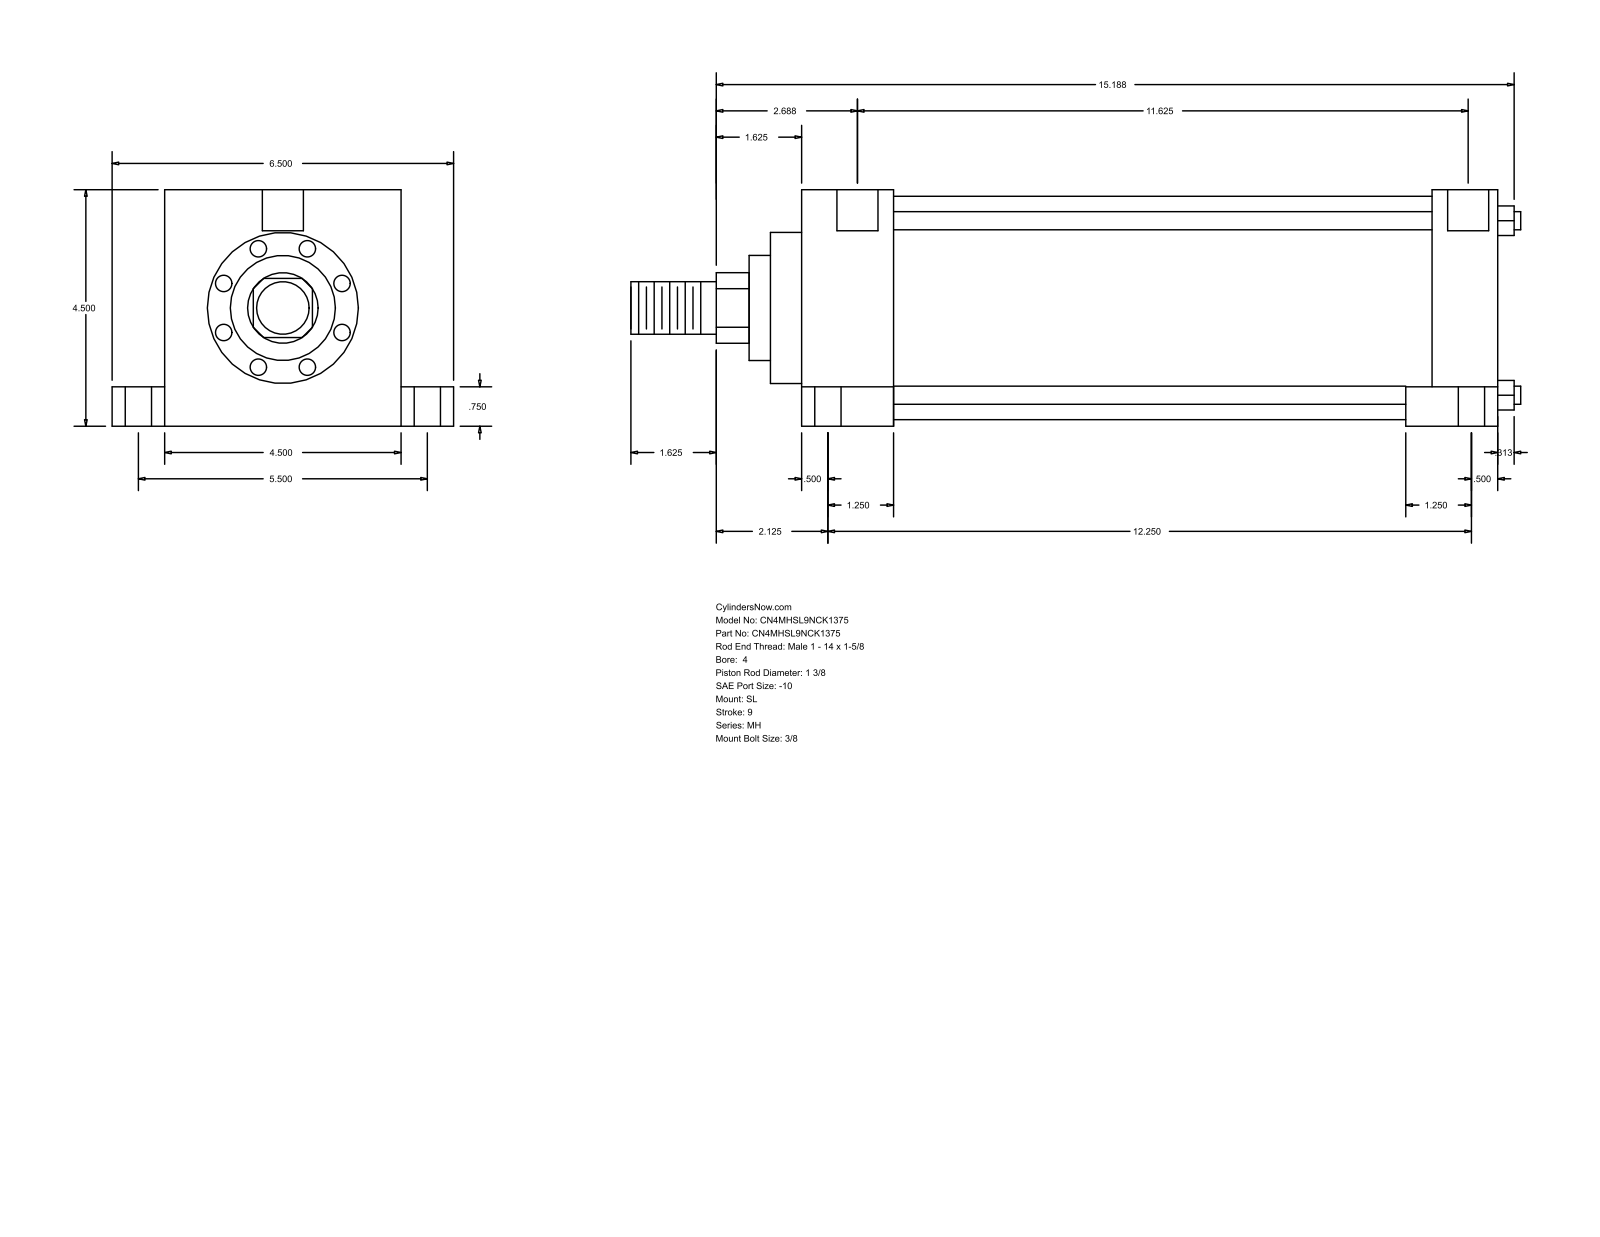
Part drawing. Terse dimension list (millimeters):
name: MH_SL__0400_1.375
written by: GSSL Pune (CONFIG_CONTROL_DESIGN)
unit: mm
bodies: 0 solids, 110 faces (77 planar, 33 cylindrical, 0 other)
size: 430.21 × 165.1 × 114.3
holes: 4× ⌀8.73, 4× ⌀12.7, 4× ⌀19.05, 2× ⌀19.84
bosses: 4× ⌀8.76, 1× ⌀107.95, 1× ⌀73.03, 1× ⌀50.8, 1× ⌀34.92, 1× ⌀25.4
rounds: 1× R17.06
face distances: 114.3, 336.55, 44.45, 292.1, 304.8, 260.35, 31.75, 25.4, 139.7, 19.05
hole spacings: 69.85, 69.87, 70.99, 71.29, 139.7, 298.45, 304.97, 306.51
